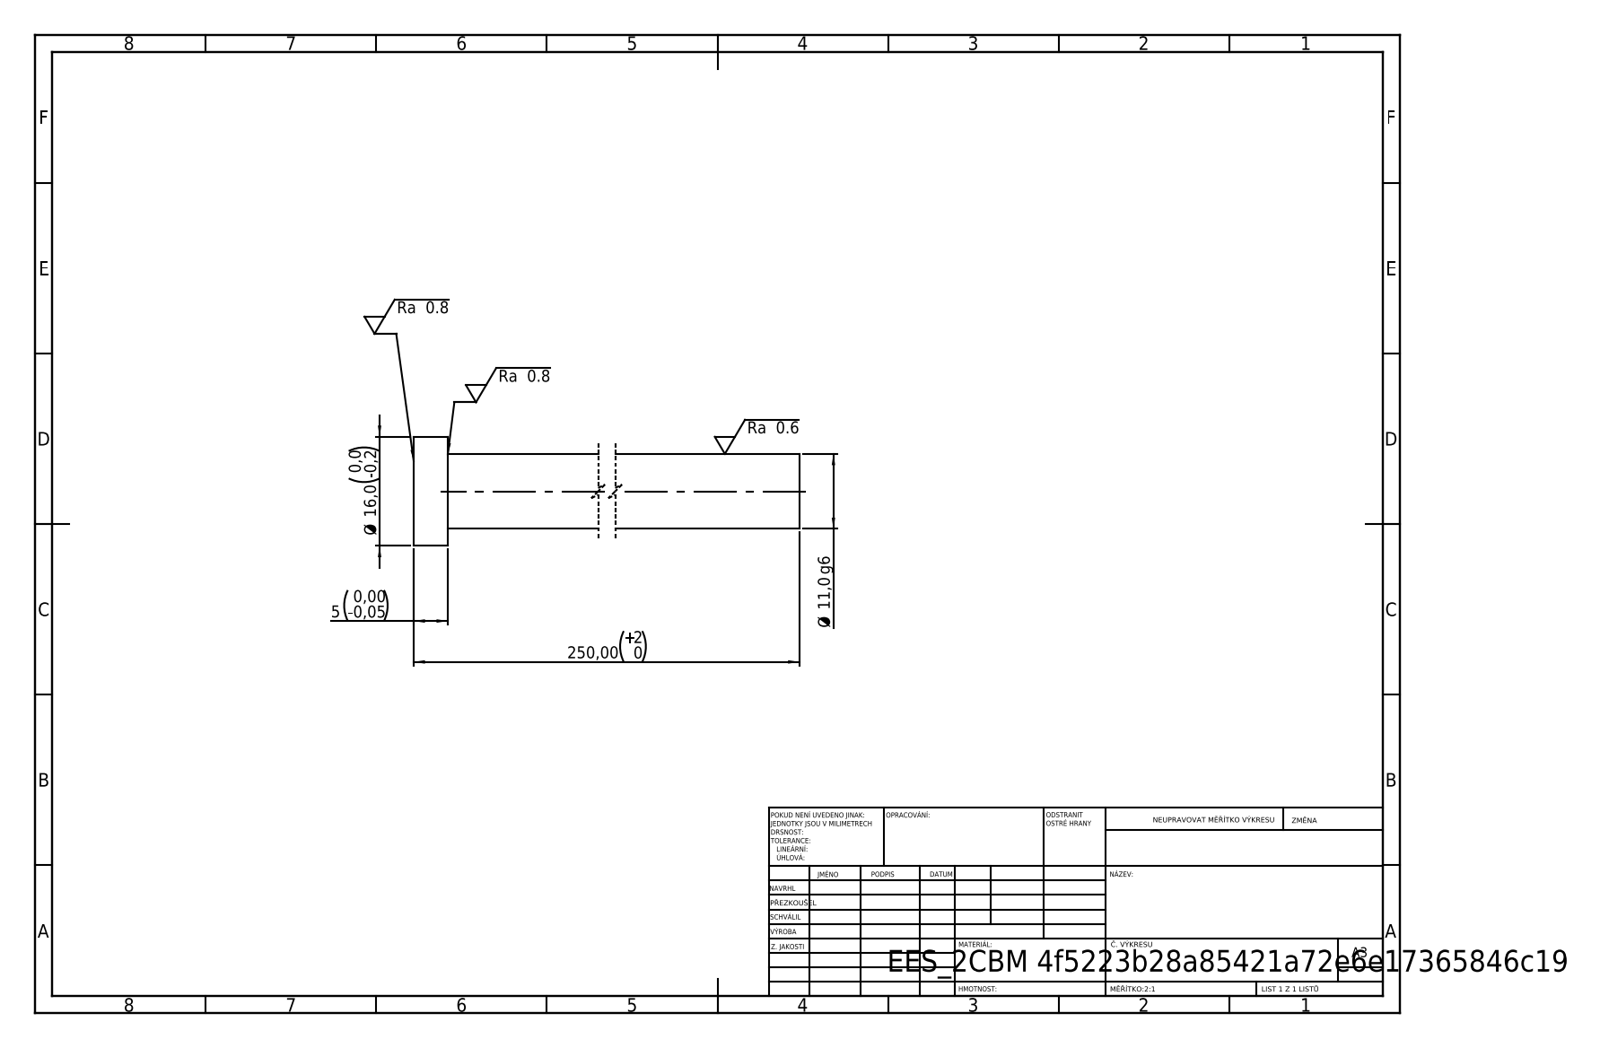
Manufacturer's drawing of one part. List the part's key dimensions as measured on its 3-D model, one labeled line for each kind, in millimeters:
STEP written by: SolidWorks 2019 (CONFIG_CONTROL_DESIGN)
Units: millimetres
Bodies: 1 solid, 7 faces (3 planar, 4 cylindrical, 0 other)
Overall size (bounding box): 250 × 16 × 16
Volume: 24 288 mm³ · Surface area: 9 120 mm²
Round bosses / shafts (diameter × count): ⌀16 ×1, ⌀11 ×1
Main face-to-face distances: 5, 250, 245
